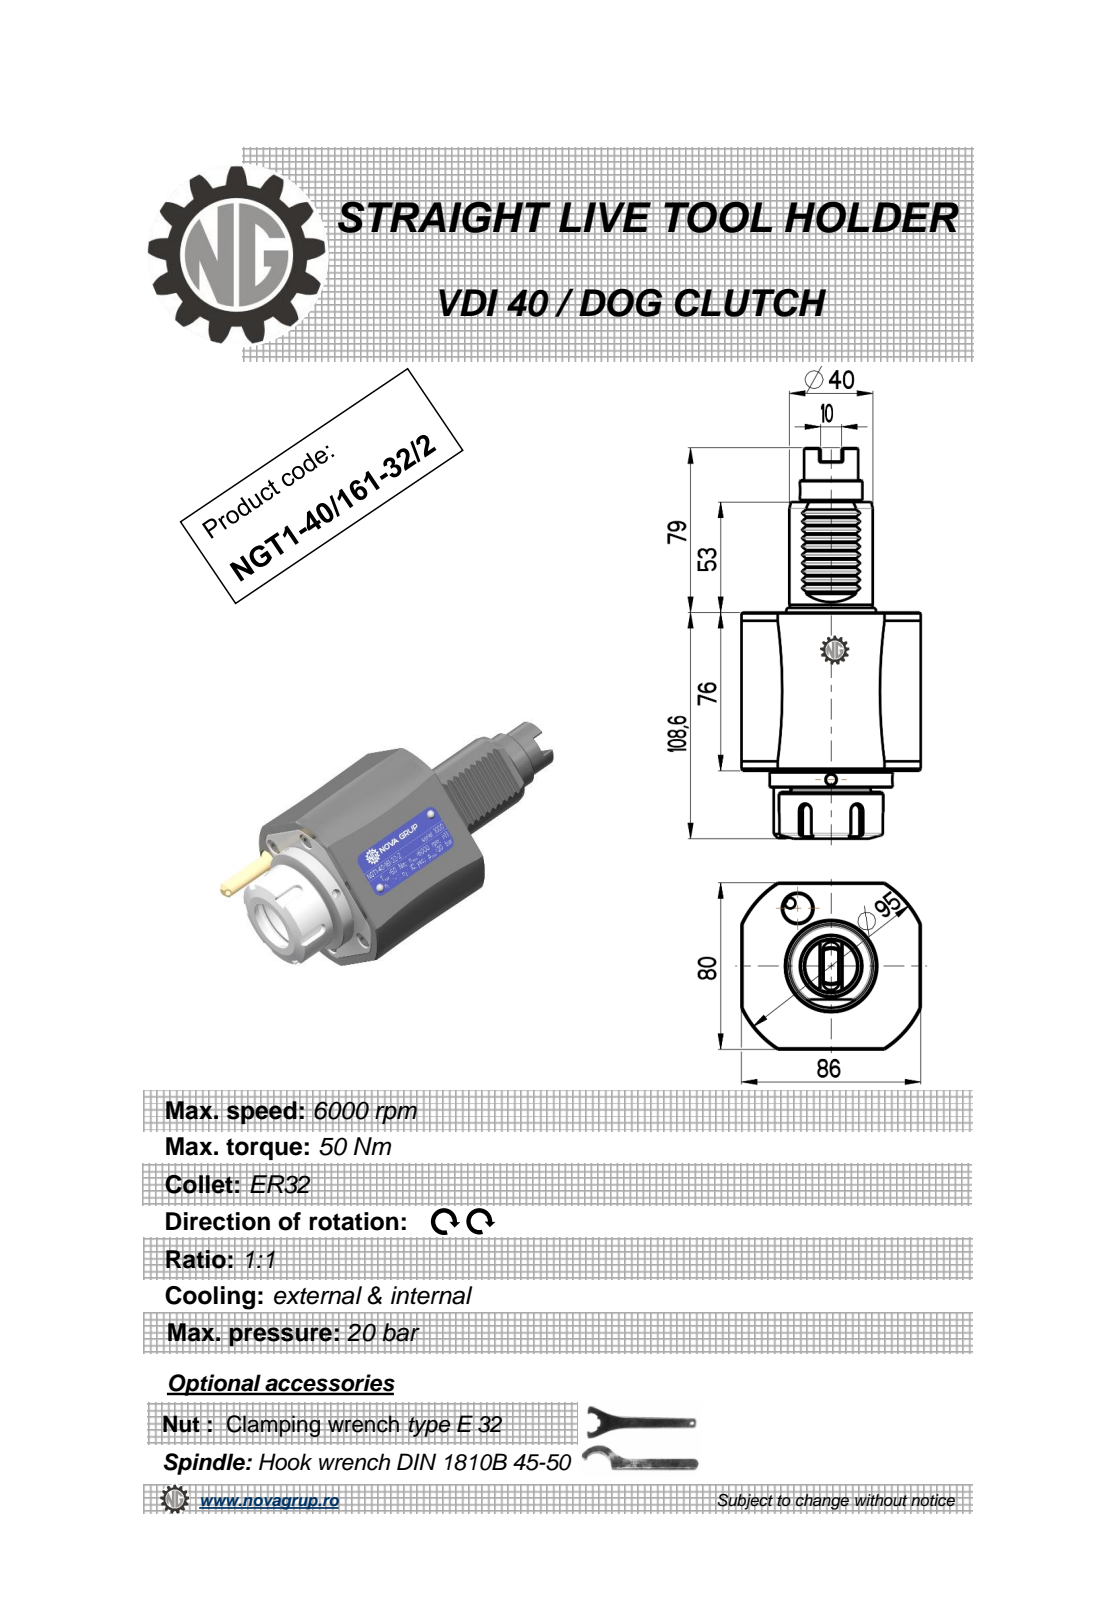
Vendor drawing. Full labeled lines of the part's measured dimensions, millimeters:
Part name (STEP PRODUCT): NGT1_40_161_32_1
STEP written by: PRO/ENGINEER BY PARAMETRIC TECHNOLOGY CORPORATION, 2010280 (CONFIG_CONTROL_DESIGN)
Units: millimetres
Bodies: 1 solid, 304 faces (113 planar, 78 cylindrical, 113 other)
Overall size (bounding box): 187.6 × 86 × 81.6
Volume: 614 987 mm³ · Surface area: 55 208 mm²
Round holes (diameter × count): ⌀5 ×3, ⌀3 ×1, ⌀4.2 ×1, ⌀27 ×1
Round bosses / shafts (diameter × count): ⌀59 ×1, ⌀50 ×1, ⌀48 ×1, ⌀41 ×1, ⌀40 ×1, ⌀30 ×1, ⌀26 ×1, ⌀8 ×1
Partial cylindrical surfaces — rounded edges, fillets, slot ends (radius × count): R0.3 ×10, R0.22 ×6, R0.26 ×6, R3 ×5, R0.5 ×2, R4 ×2, R9 ×1, R47.5 ×1
Main face-to-face distances: 76, 80, 86, 84, 8, 0.5, 7.5, 2.83, 76.5, 104.1
Hole centre spacings: 40, 138.75
